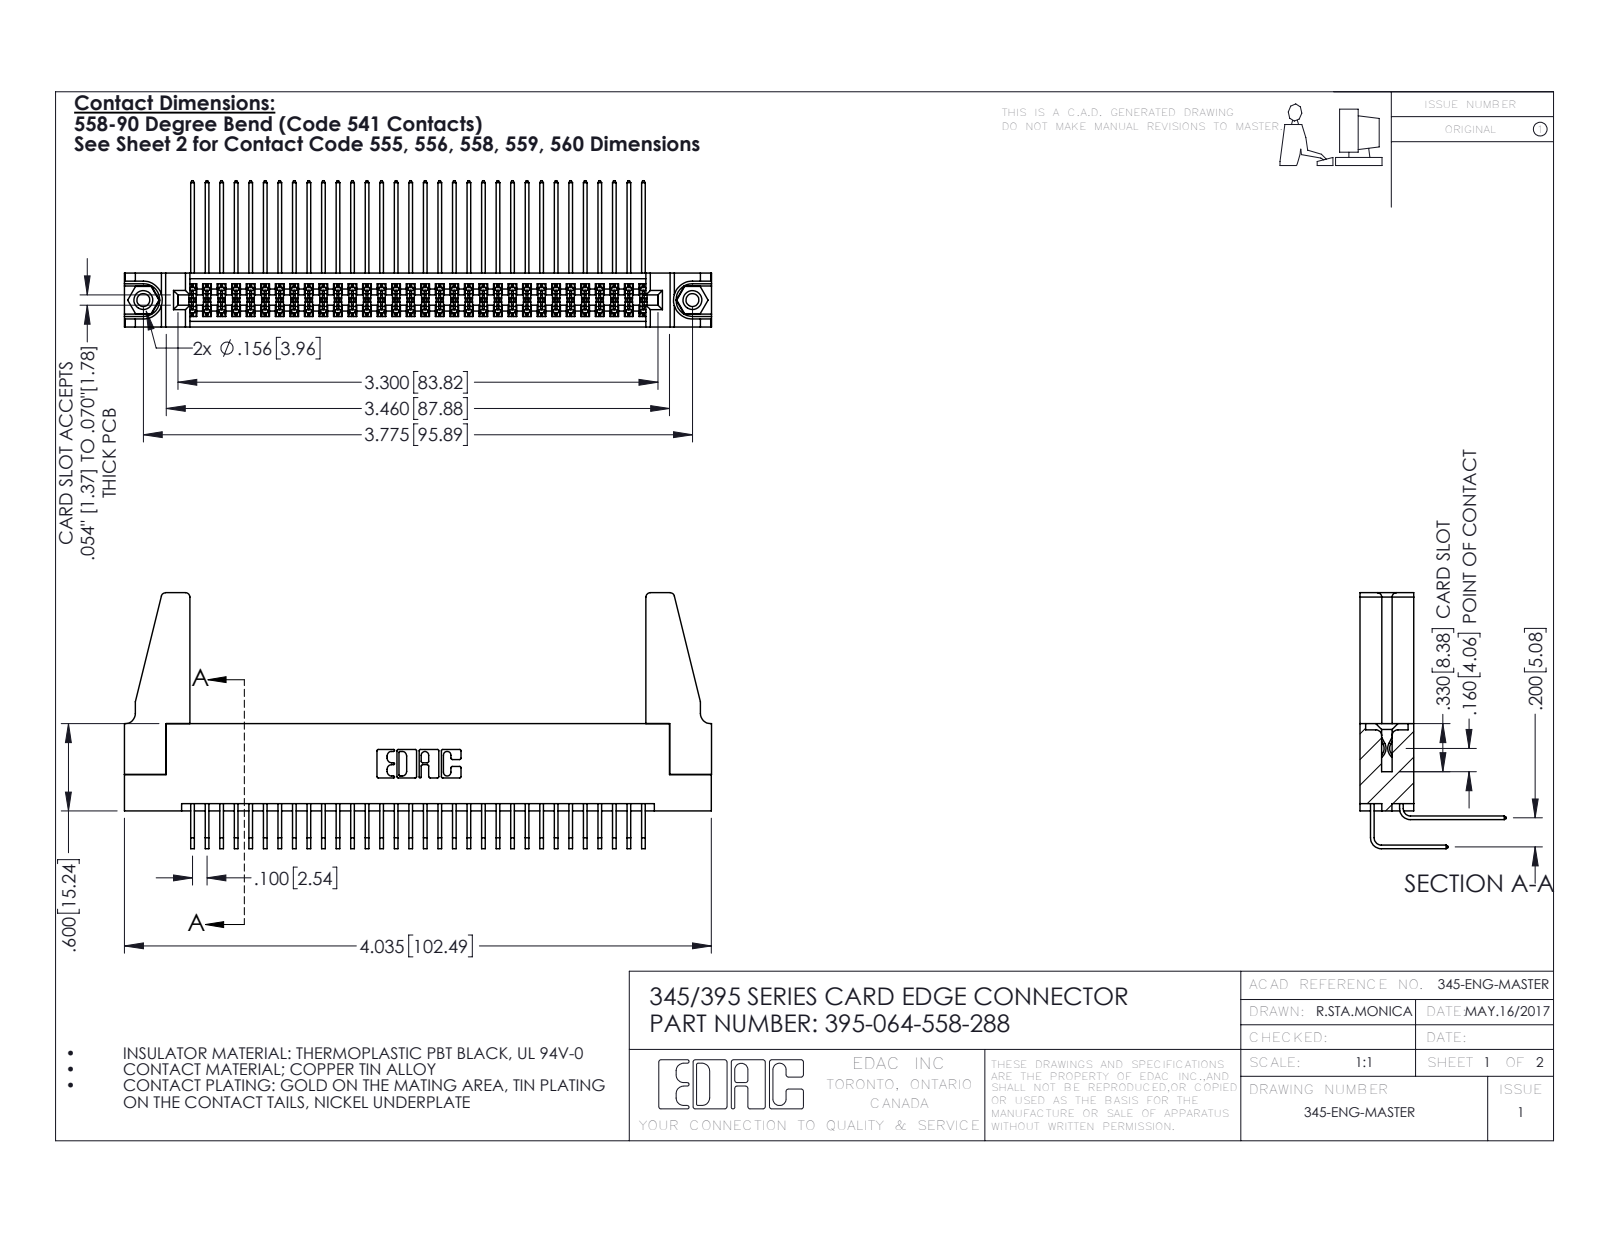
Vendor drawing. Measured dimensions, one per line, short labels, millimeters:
name: 345-292-001_558 559 Tail - 1; 345 Part_Flush Mounting Lugs - 0.156 Dia-TH; 345-292-001_558 Tail - 2; 345-220-078_345-220-088 (+2 more)
written by: SolidWorks 2016 (CONFIG_CONTROL_DESIGN)
unit: mm
bodies: 69 solids, 3578 faces (2392 planar, 1170 cylindrical, 16 other)
size: 102.5 × 44.7 × 25.5
volume: 13 500 mm³; area: 19 790 mm²
holes: 2× ⌀2.3, 2× ⌀3.2, 2× ⌀4, 1× ⌀1.6
bosses: 2× ⌀3.9
rounds: 97× R0.2, 22× R0.3, 8× R0.8, 6× R0.2, 6× R0.8, 3× R0.7, 2× R0.4, 2× R0.5
face distances: 1.8, 7.6, 5.1, 9.4, 2.5, 6.9, 0.6, 5.7, 7.2, 0.6
hole spacings: 6.9, 89.9, 95.9
